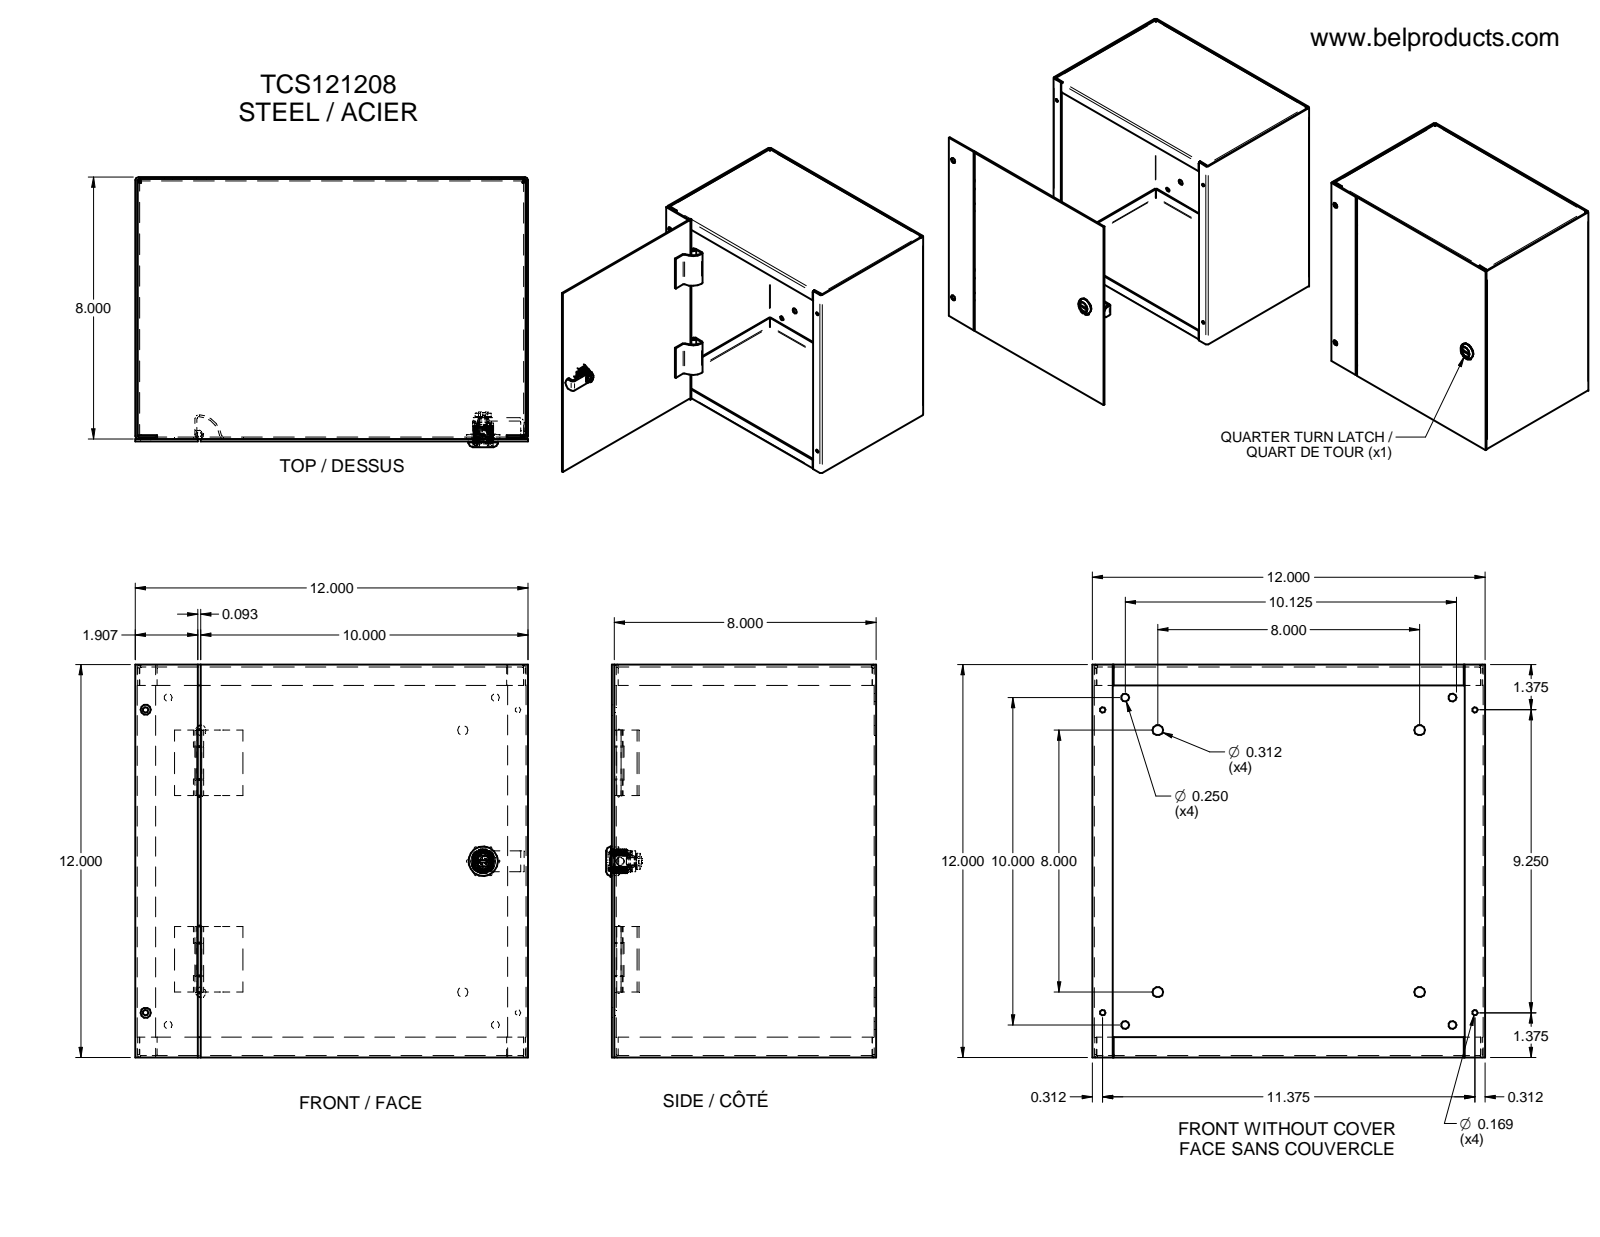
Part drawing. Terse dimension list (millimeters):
name: LOCK AVEC TOURNEVIS TYPE 4-12 SANS CAME; HOSING-oa0; INSERT POUR TOURNEVIS-oa1; NOIX DE FIXATION-oa2 (+8 more)
written by: Unknown (AUTOMOTIVE_DESIGN)
unit: mm
bodies: 18 solids, 631 faces (324 planar, 161 cylindrical, 146 other)
size: 304.8 × 304.8 × 209.57
volume: 762 955 mm³; area: 965 079 mm²
holes: 6× ⌀7.92, 4× ⌀4.29, 4× ⌀6.35, 1× ⌀3.81, 1× ⌀6.99, 1× ⌀9.1, 1× ⌀11.18, 1× ⌀12.83, 1× ⌀15.8, 1× ⌀17.46
bosses: 1× ⌀22.86, 1× ⌀22.61, 1× ⌀15.75, 1× ⌀12.95, 1× ⌀12.62, 1× ⌀12.19, 1× ⌀11.86, 1× ⌀10.08
rounds: 13× R0.81, 12× R2.34, 12× R9.53, 8× R0.25, 2× R1.52, 2× R3.05, 2× R9.42, 1× R3.48
face distances: 1.52, 303.28, 304.8, 301.76, 201.68, 203.2, 1.91, 203.59, 205.11, 1.92
hole spacings: 230.01, 19.89, 246.57, 271.63, 365.32, 35.92, 45.7, 203.2
